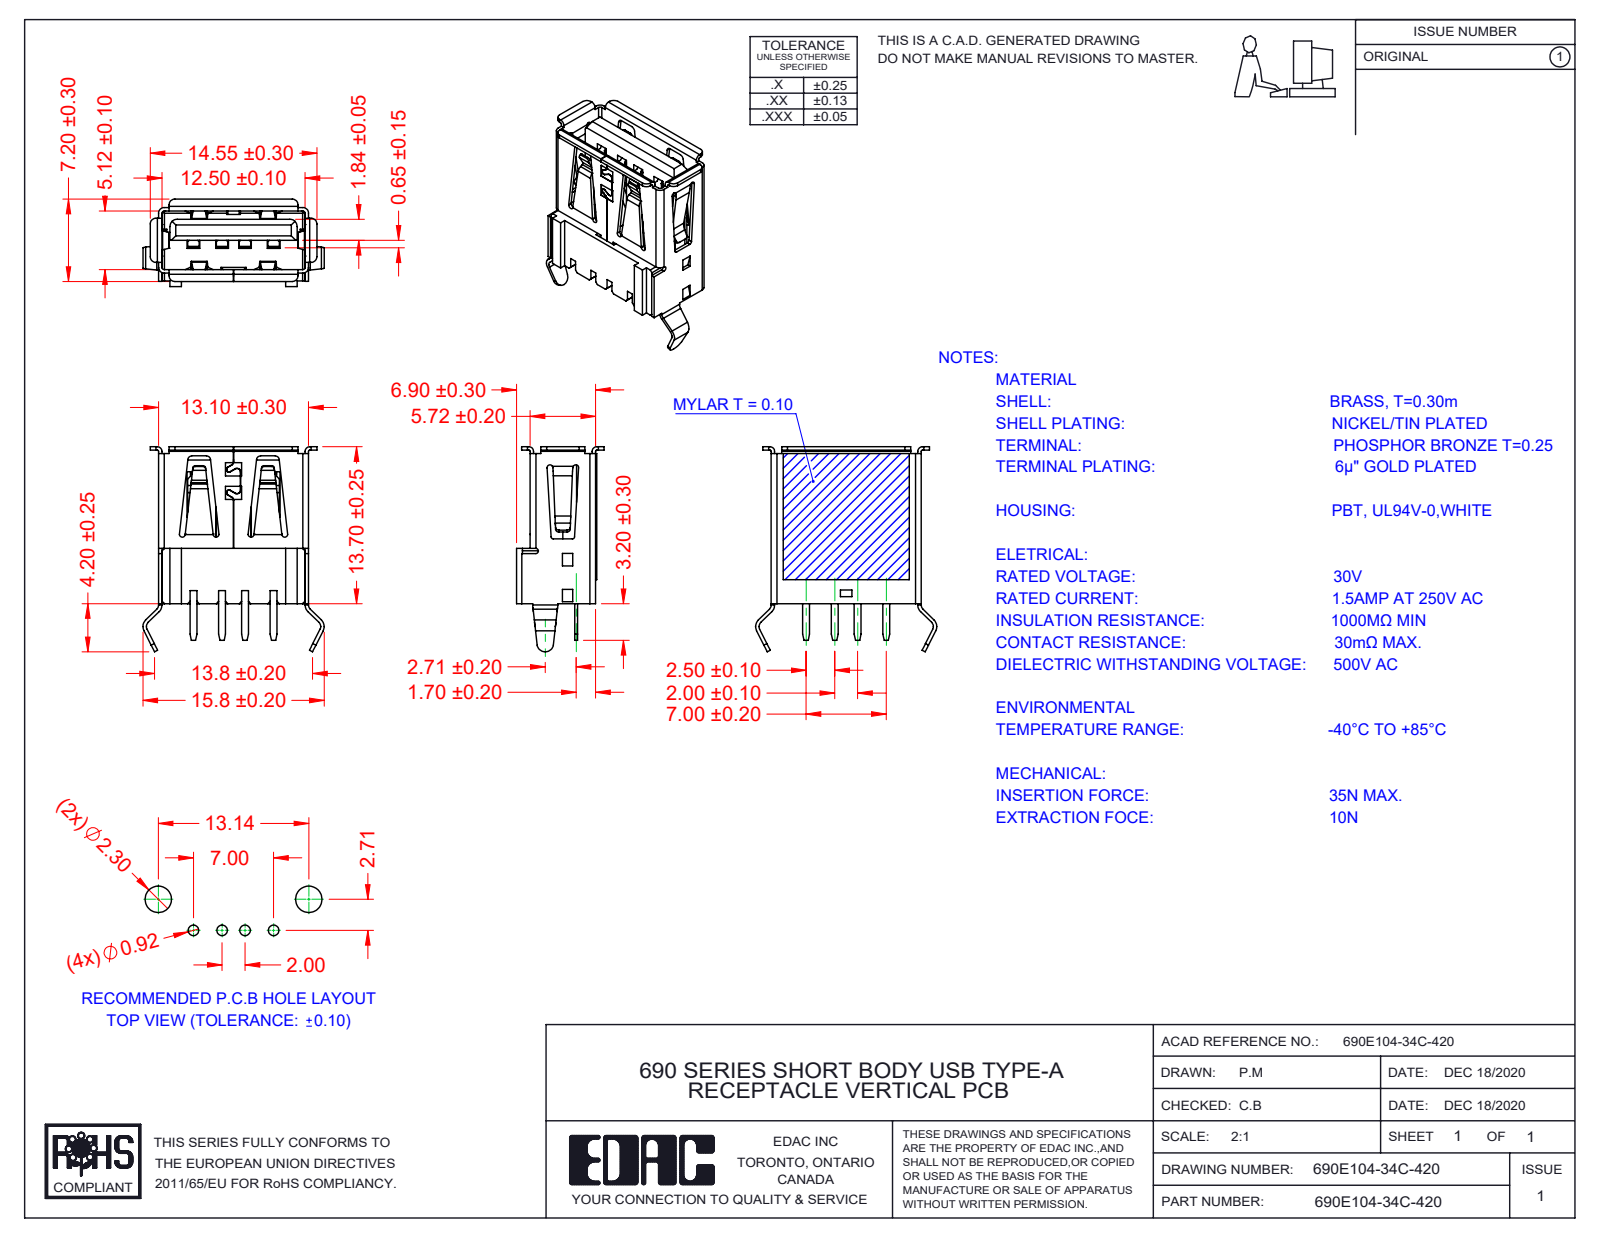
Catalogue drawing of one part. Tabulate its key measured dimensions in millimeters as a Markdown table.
| quantity | value |
| --- | --- |
| part name | 690E104-24C-420; Insulator 690E104-X4C-42X_White; Contact 690E104-X4C-42X; Shell 690E104-X4C-42X (+1 more) |
| STEP written by | SolidWorks 2020 (AUTOMOTIVE_DESIGN) |
| units | millimeters |
| bodies | 7 solids, 742 faces (558 planar, 184 cylindrical, 0 other) |
| overall size | 17.9 × 15.82 × 7.64 |
| volume | 571 mm³ |
| surface area | 2 137 mm² |
| partial cylindrical surfaces (radius × count) | 0.2 × 31, 0.15 × 18, 0.5 × 16, 0.3 × 11, 0.25 × 6, 0.4 × 5, 0.1 × 4, 0.18 × 4 |
| main face-to-face distances | 5.42, 0.4, 2.56, 3.6, 2.86, 2.5, 12.8, 4.7, 1.57, 1.67 |
